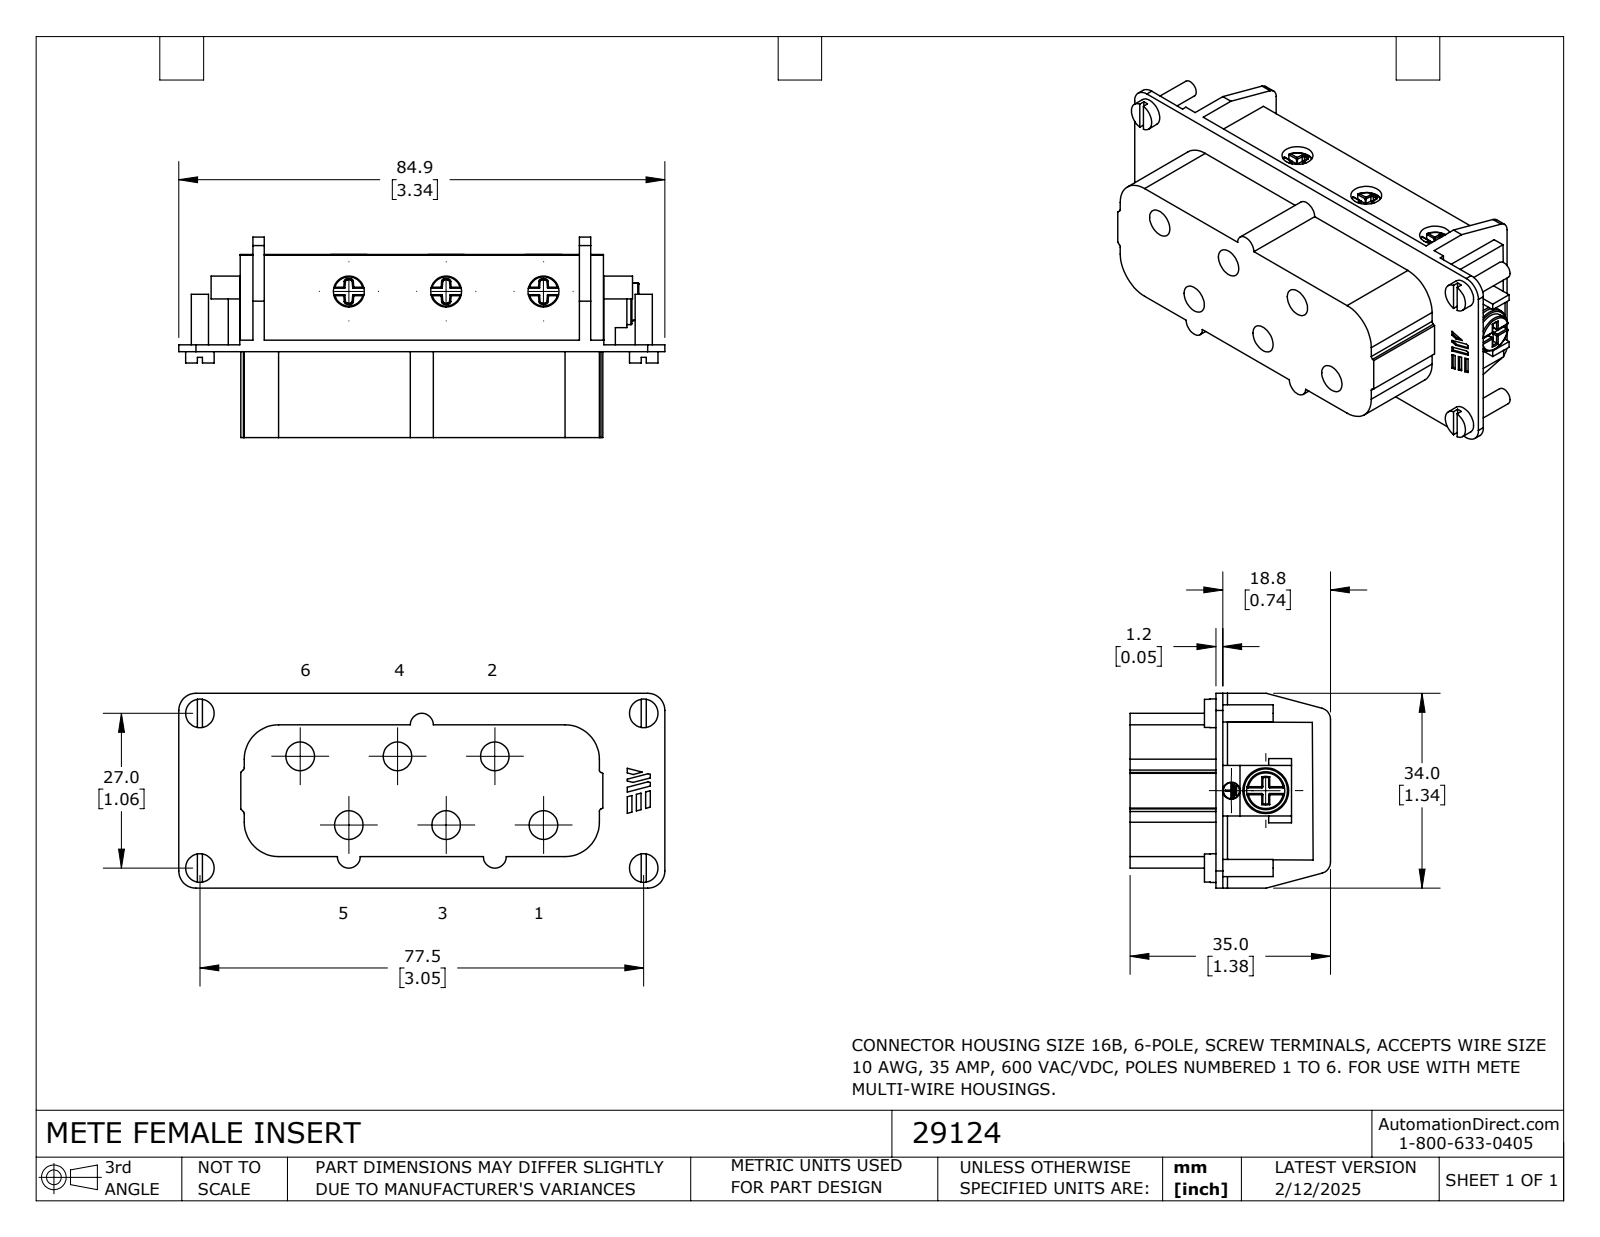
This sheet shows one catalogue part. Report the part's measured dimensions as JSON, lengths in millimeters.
{"part_name": "29124", "step_written_by": "SolidWorks 2024 (CONFIG_CONTROL_DESIGN)", "units": "millimeters", "bodies": {"solids": 1, "faces": 606, "planar": 284, "cylindrical": 200, "other": 122}, "overall_size": [84.9, 35, 34], "volume_mm3": 46030, "surface_area_mm2": 17930, "round_holes": [[5, 6], [5.4, 6], [3, 1]], "round_bosses_or_shafts": [[3, 10], [5, 4], [8, 1], [6.6, 1], [2.8, 1]], "partial_cylinders_radius": [[0.2, 56], [3.4, 6], [0.5, 4], [3, 4], [6, 4], [2, 3], [2, 2], [2.3, 1]], "face_to_face_distances": [15, 2, 0.8, 1.2, 24, 16.2, 17, 2.2, 23, 63.4], "hole_center_spacings": [17, 8.5, 14.7, 34, 25.5, 28.2, 42.5, 44.2]}
